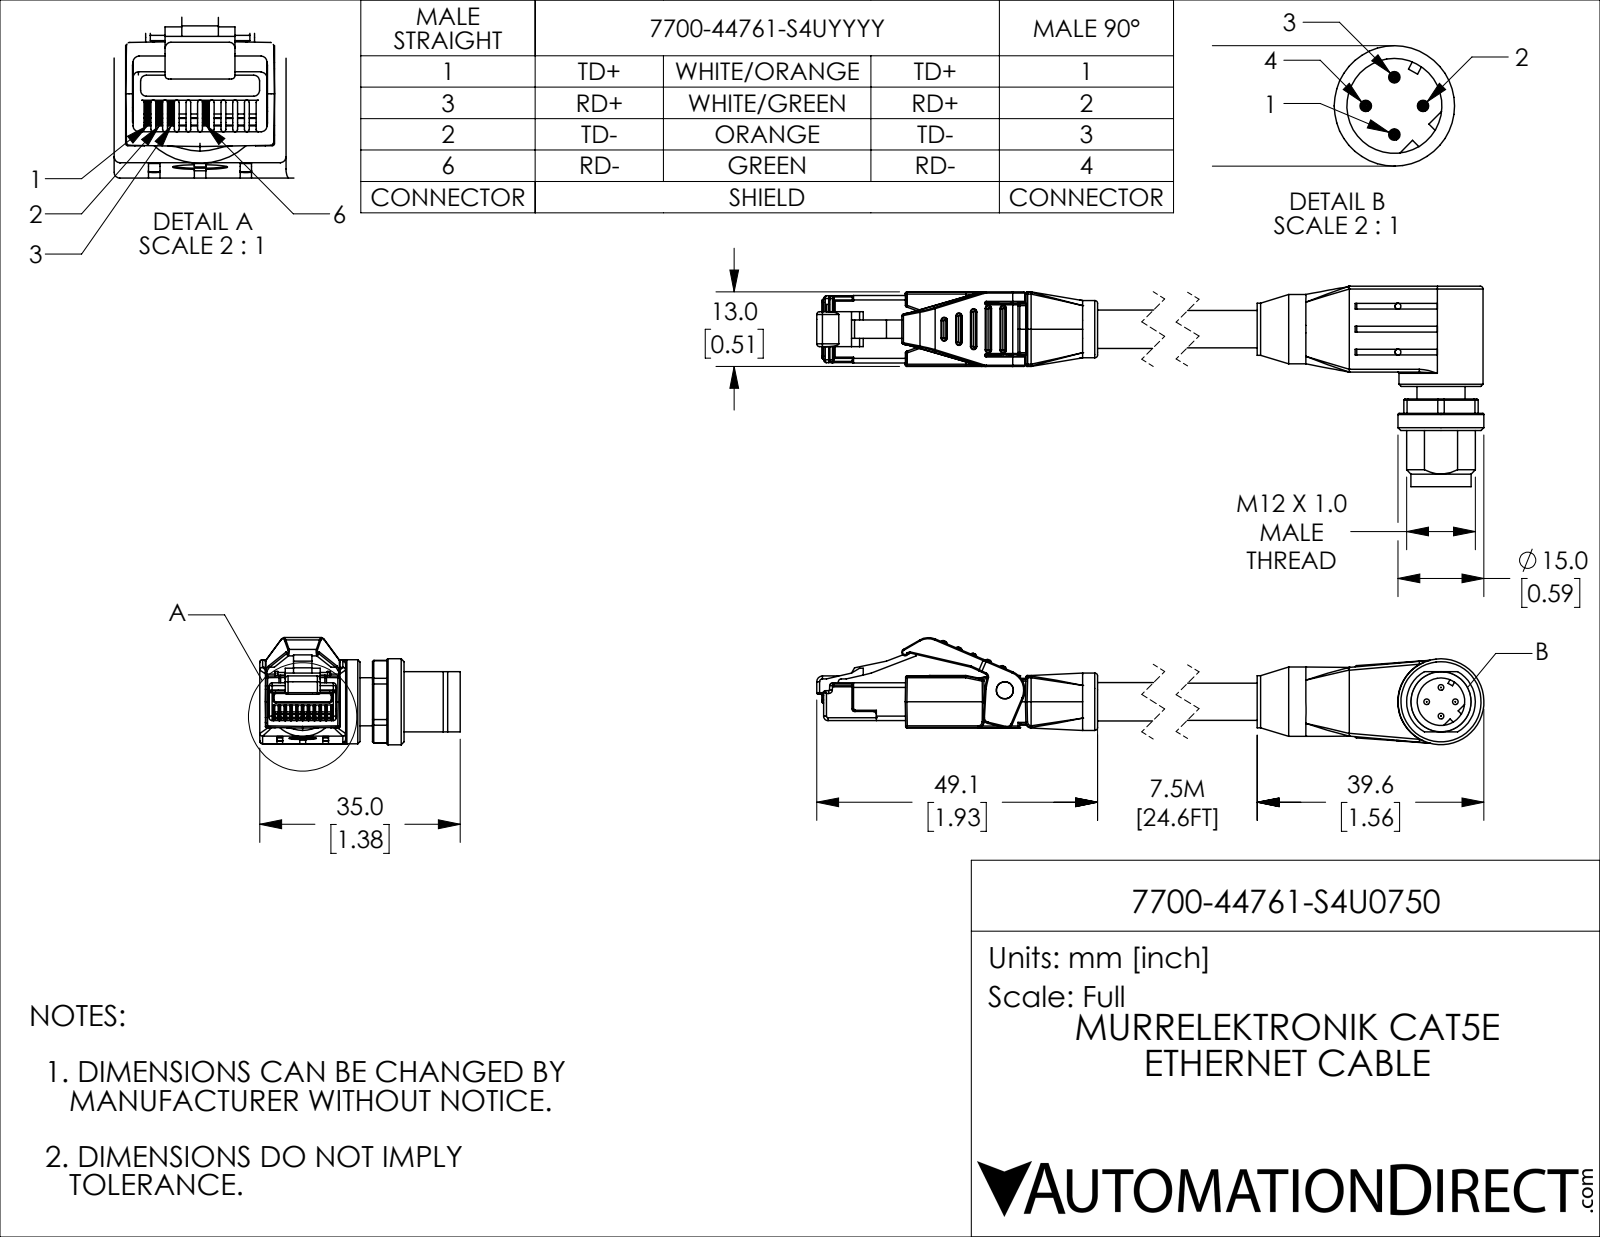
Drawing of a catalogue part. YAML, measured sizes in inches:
part_name: "7700-44761-S4U0750; 7700-44761-S4U0750_2; 7700-44761-S4U0750_1"
step_written_by: "SolidWorks 2021 (CONFIG_CONTROL_DESIGN)"
units: inches
bodies: {solids: 3, faces: 883, planar: 369, cylindrical: 338, other: 176}
overall_size: [5.778, 1.378, 0.736]
volume: 0.915
surface_area: 11.82
round_holes:
  - {diameter: 0.041, count: 4}
  - {diameter: 0.118, count: 1}
  - {diameter: 0.189, count: 1}
  - {diameter: 0.327, count: 1}
round_bosses_or_shafts:
  - {diameter: 0.039, count: 4}
  - {diameter: 0.591, count: 1}
  - {diameter: 0.579, count: 1}
  - {diameter: 0.476, count: 1}
  - {diameter: 0.413, count: 1}
  - {diameter: 0.394, count: 1}
  - {diameter: 0.358, count: 1}
  - {diameter: 0.331, count: 1}
partial_cylinders:
  - {radius: 0.008, count: 82}
  - {radius: 0.012, count: 67}
  - {radius: 0.02, count: 28}
  - {radius: 0.004, count: 20}
  - {radius: 0.031, count: 5}
  - {radius: 0.039, count: 5}
  - {radius: 0.079, count: 2}
  - {radius: 0.197, count: 2}
face_to_face_distances: [0.512, 0.362, 0.039, 0.689, 0.098, 0.551, 0.591, 0.185, 0.077, 0.337]
hole_center_spacings: [0.315, 4.19]
